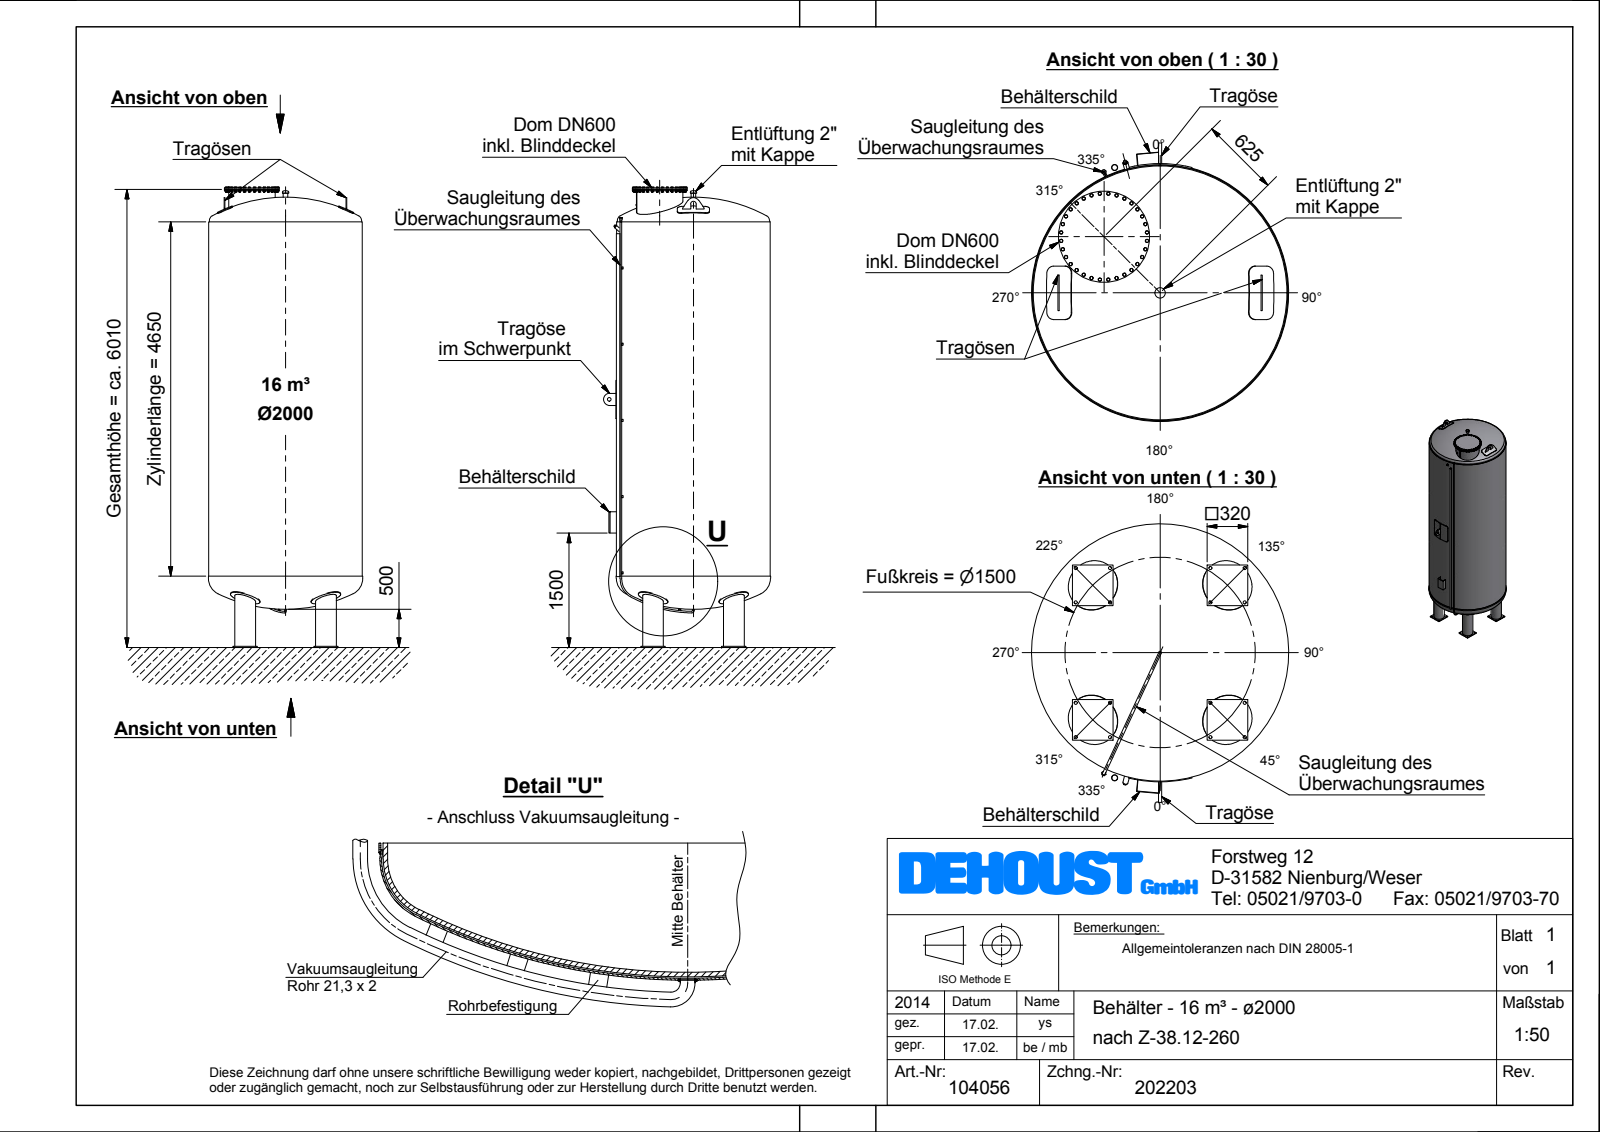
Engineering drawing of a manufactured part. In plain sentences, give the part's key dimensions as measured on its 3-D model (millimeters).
The part is named "Z-38_12-260_Beh\\S\\dlter_\\S\\x2000_016m\\S\\3_Dichte=1,0". Its 3-D file was written by "Autodesk Inventor 2012 (AUTOMOTIVE_DESIGN)". It is 9 solids with 1171 faces: 693 planar, 150 cylindrical and 328 other. Overall it measures 6039.18 by 2193 by 2026 millimeters. Its volume is 15 880 000 000 cubic millimeters and its surface area 53 000 000 square millimeters. Round holes: 4 of diameter 257, 1 of diameter 598, 1 of diameter 1988. Round bosses or shafts: 32 of diameter 22.5, 32 of diameter 16, 4 of diameter 400, 4 of diameter 273, 2 of diameter 21.3, 1 of diameter 2026, 1 of diameter 2016, 1 of diameter 2000. Partial cylindrical surfaces (rounded edges, fillets, slot ends): 8 of radius 56, 4 of radius 50, 1 of radius 35, 1 of radius 80, 1 of radius 85, 1 of radius 1018. The main face-to-face distances are 5584.39, 6029.17, 444.78, 5994.17, 409.78, 35, 15, 5569.39, 5979.17, 6014.17. The hole center spacings are 750, 1060.66, 976.28, 1500, 125, 625, 1375.
